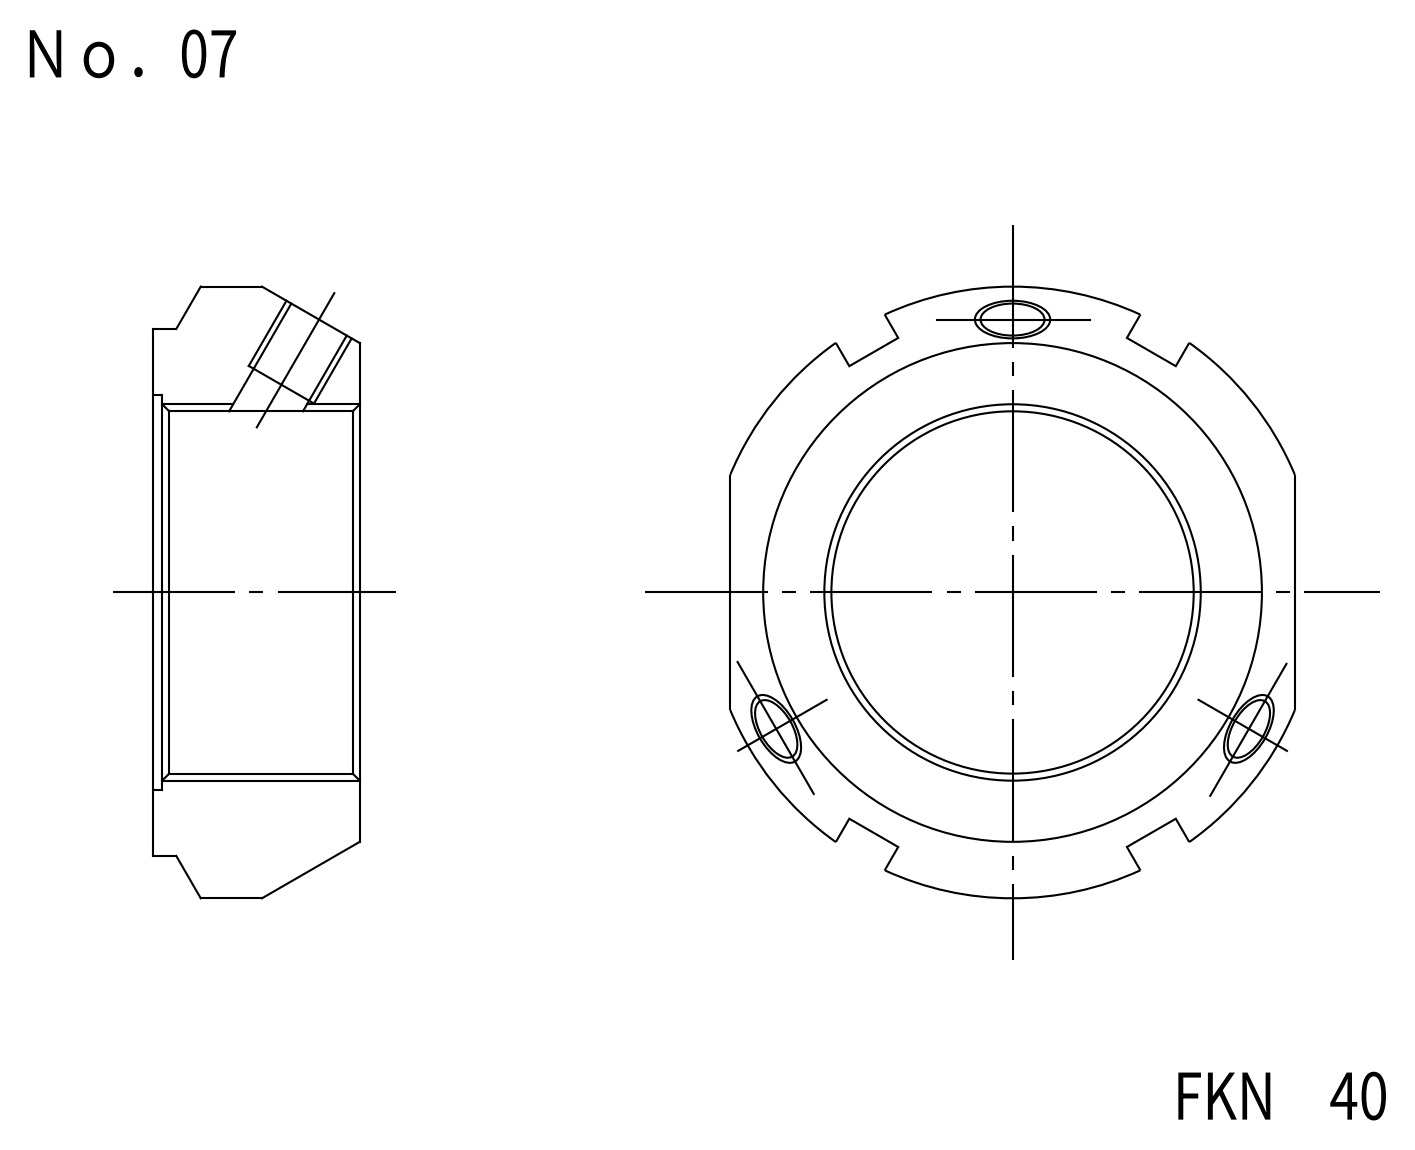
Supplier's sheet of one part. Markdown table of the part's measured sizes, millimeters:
| quantity | value |
| --- | --- |
| part name | FKD FKN40 |
| STEP written by | Autodesk Inventor LT (CONFIG_CONTROL_DESIGN) |
| units | millimeters |
| bodies | 1 solid, 37 faces (20 planar, 15 cylindrical, 2 other) |
| overall size | 65 × 60 × 22 |
| volume | 33 371 mm³ |
| surface area | 10 423 mm² |
| round holes (diameter × count) | 6.65 × 3, 8.1 × 3, 40 × 1, 42 × 1 |
| round bosses / shafts (diameter × count) | 56 × 1 |
| partial cylindrical surfaces (radius × count) | 32.5 × 1 |
| main face-to-face distances | 22, 60, 59, 1.5, 20.5, 6 |
